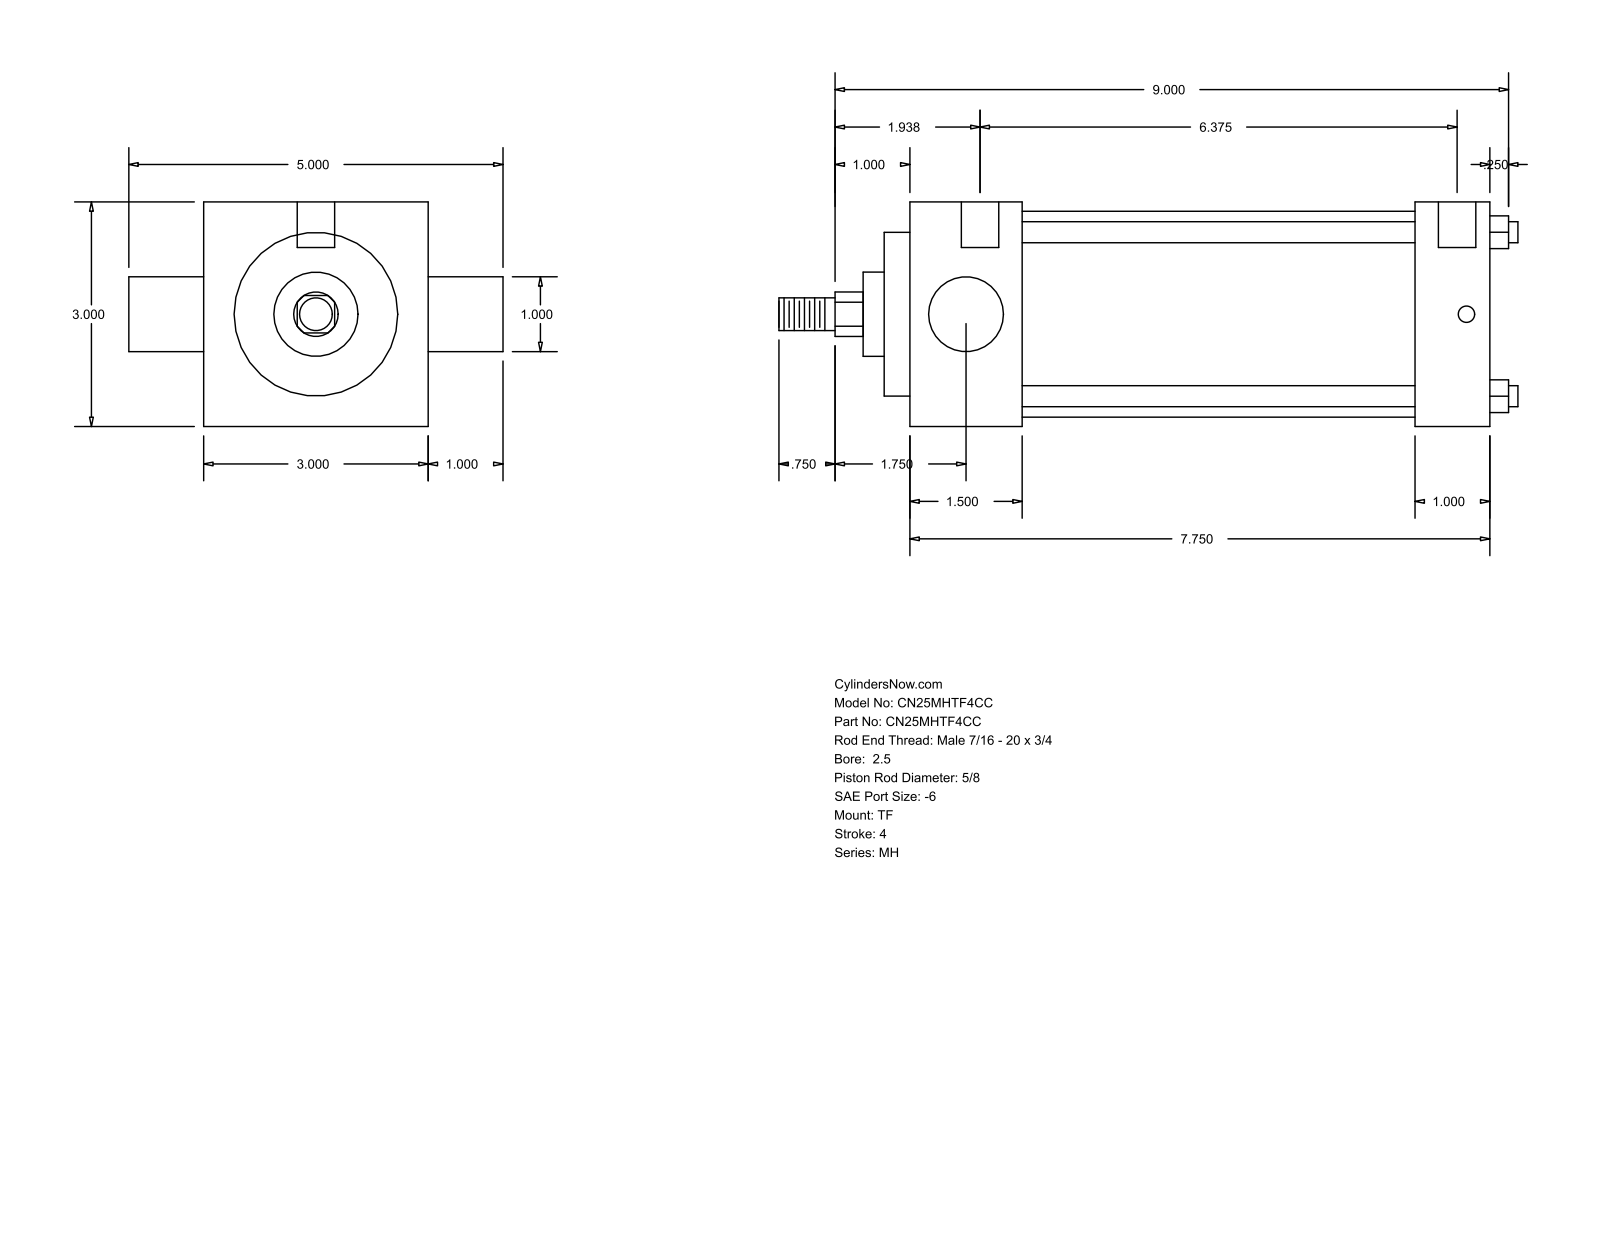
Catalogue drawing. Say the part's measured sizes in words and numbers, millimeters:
The part is named "MH_TF__0250_0.625". Its 3-D file was written by "GSSL Pune (CONFIG_CONTROL_DESIGN)". It is 0 solids with 86 faces: 61 planar, 25 cylindrical and 0 other. Overall it measures 250.82 by 127 by 76.2 millimeters. Round holes: 3 of diameter 5.56, 2 of diameter 12.7. Round bosses or shafts: 4 of diameter 7.14, 1 of diameter 69.85, 1 of diameter 55.55, 1 of diameter 28.57, 1 of diameter 25.4, 1 of diameter 15.88, 1 of diameter 11.11. Partial cylindrical surfaces (rounded edges, fillets, slot ends): 1 of radius 7.54. The main face-to-face distances are 76.2, 196.85, 25.4, 38.1, 158.75, 171.45, 133.35, 8.73, 46.83, 180.18. The hole center spacings are 3.17, 4.76, 161.93, 165.1, 166.69, 169.86.
